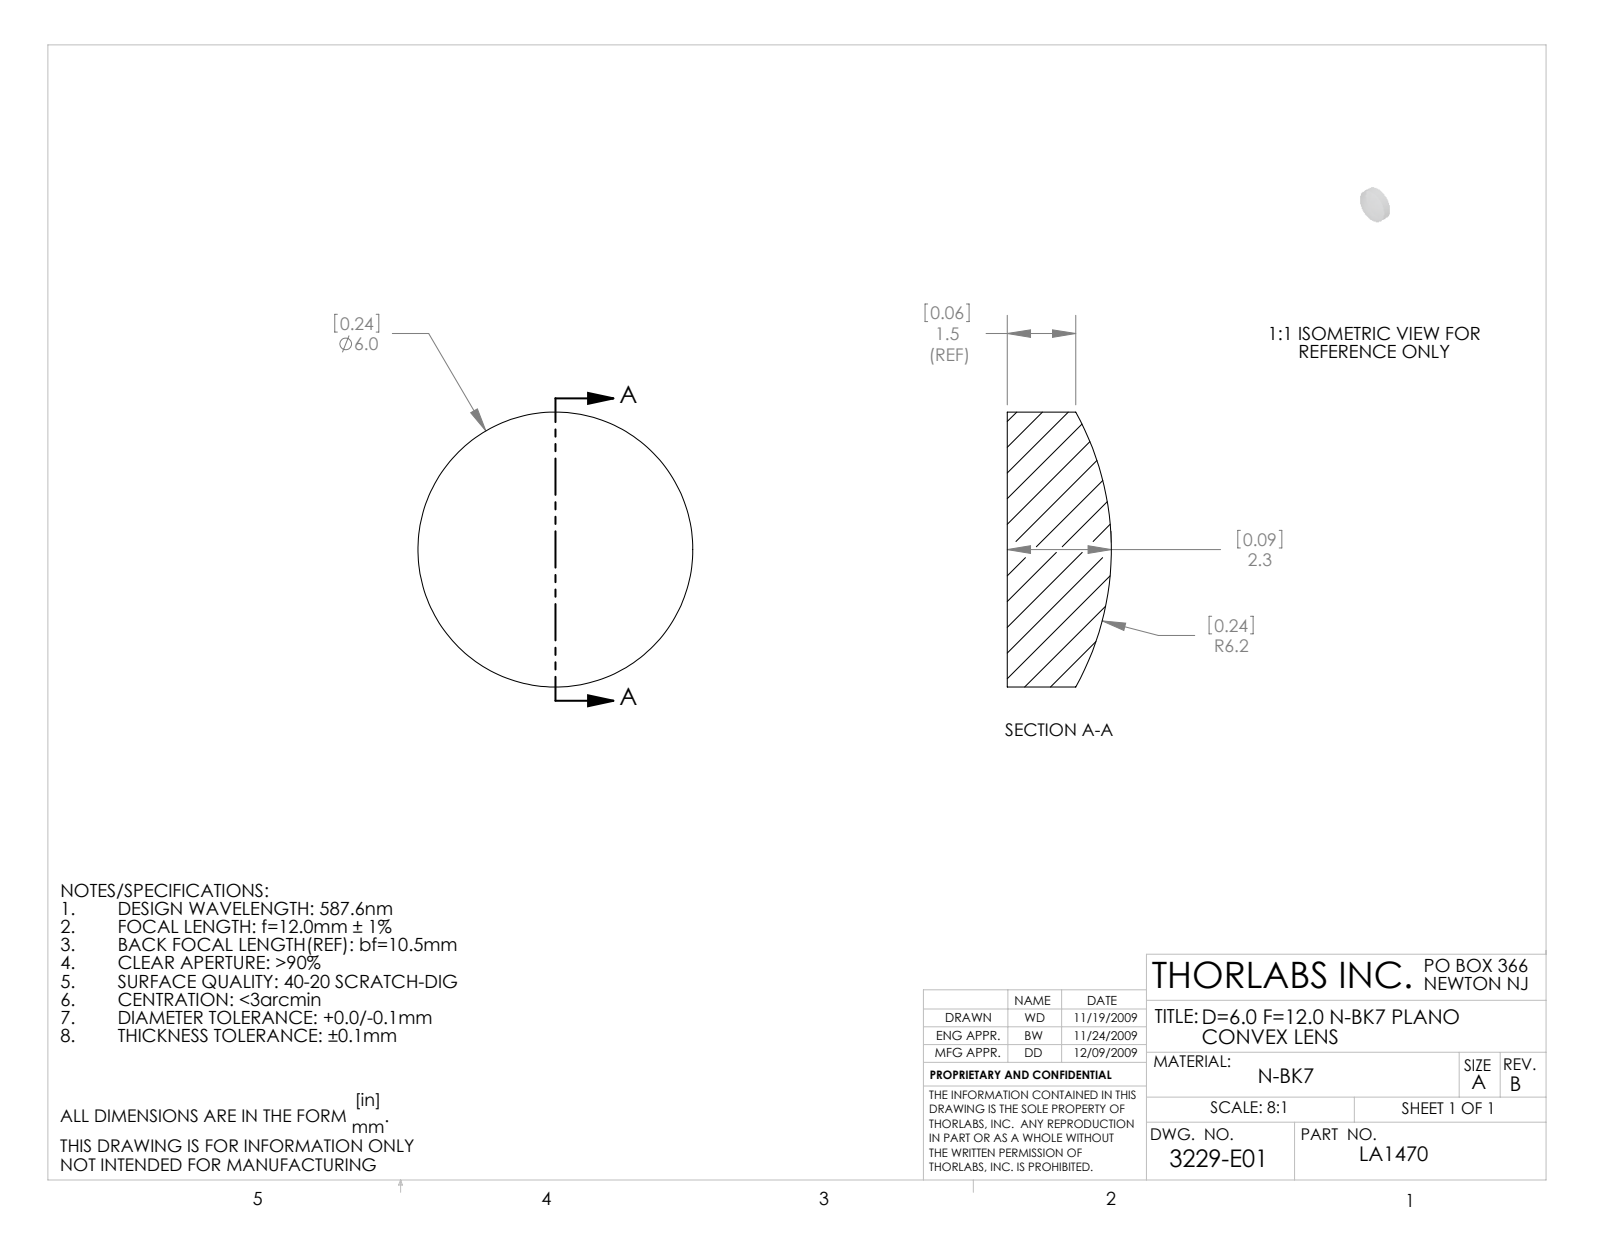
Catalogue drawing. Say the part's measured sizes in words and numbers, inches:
The part is named "3229-E0W". Its 3-D file was written by "SolidWorks 2009 (AUTOMOTIVE_DESIGN)". It is 1 solid with 5 faces: 1 planar, 2 cylindrical and 2 other. Overall it measures 0.236 by 0.236 by 0.089 inches. Its volume is 0.003 cubic inches and its surface area 0.13 square inches. Round bosses or shafts: 1 of diameter 0.236.
